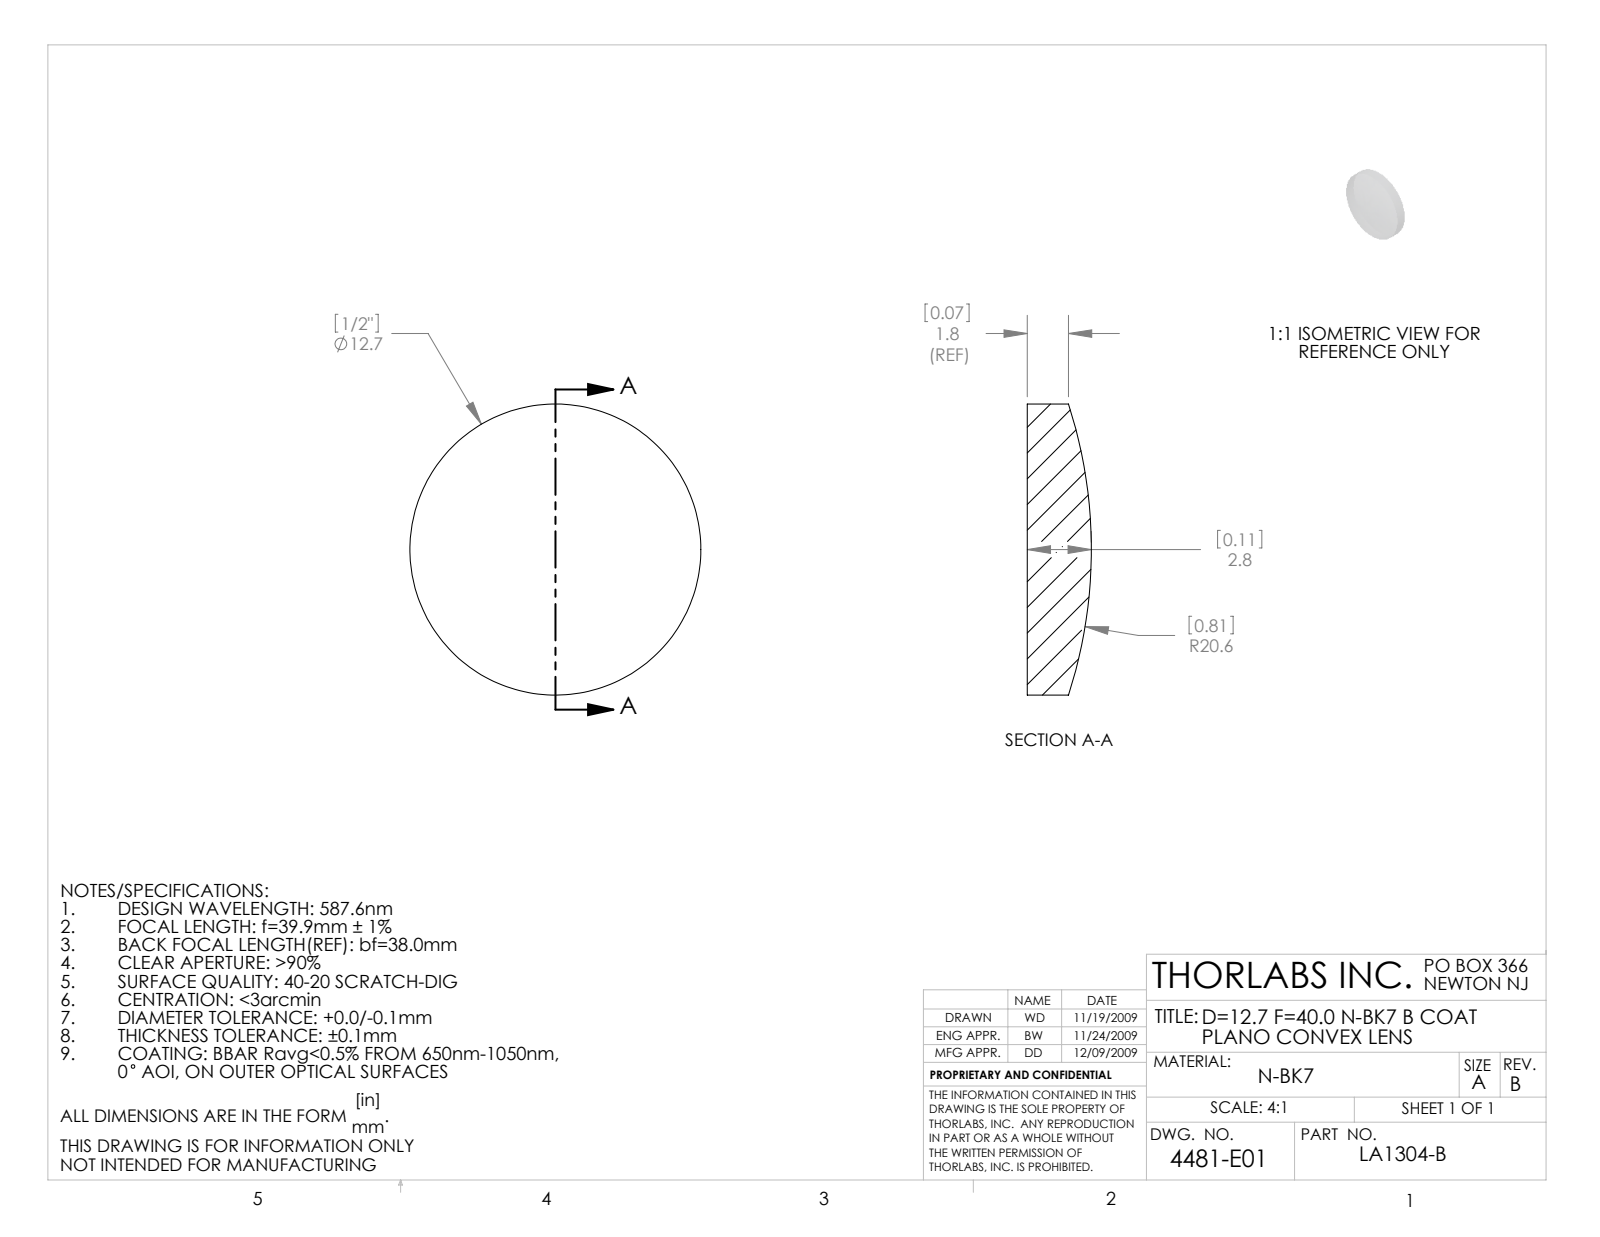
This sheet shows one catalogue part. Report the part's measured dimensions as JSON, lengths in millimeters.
{"part_name": "4481-E0W", "step_written_by": "SolidWorks 2009 (AUTOMOTIVE_DESIGN)", "units": "millimeters", "bodies": {"solids": 1, "faces": 5, "planar": 1, "cylindrical": 2, "other": 2}, "overall_size": [12.7, 12.7, 2.8], "volume_mm3": 292, "surface_area_mm2": 328, "round_bosses_or_shafts": [[12.7, 1]]}
